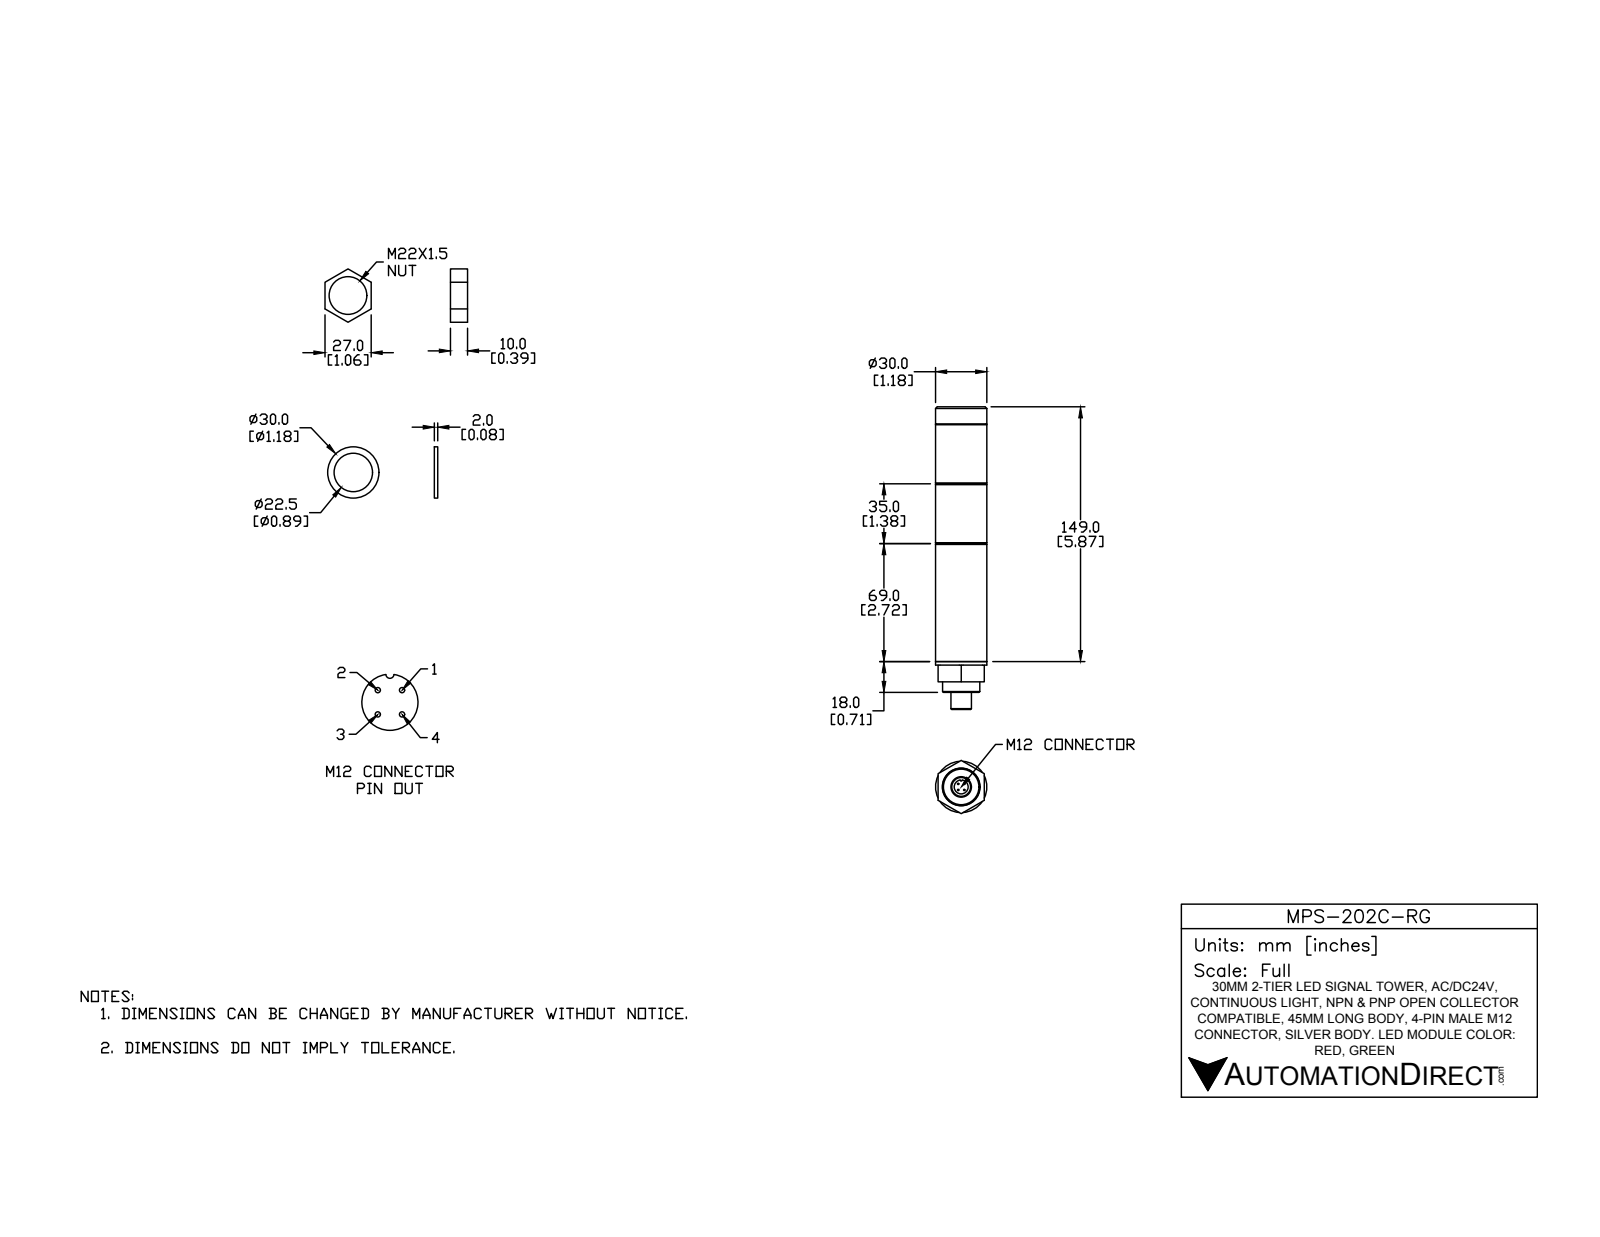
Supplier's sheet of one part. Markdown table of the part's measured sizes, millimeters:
| quantity | value |
| --- | --- |
| part name | MPS-202C-RG |
| STEP written by | SolidWorks 2016 (AUTOMOTIVE_DESIGN) |
| units | millimeters |
| bodies | 11 solids, 106 faces (43 planar, 37 cylindrical, 26 other) |
| overall size | 177 × 31.18 × 30 |
| volume | 104 467 mm³ |
| surface area | 27 501 mm² |
| round holes (diameter × count) | 3.2 × 1, 7.7 × 1, 8.2 × 1, 20.7 × 1, 22 × 1 |
| round bosses / shafts (diameter × count) | 0.75 × 4, 30 × 1, 21.8 × 1, 12 × 1, 5 × 1 |
| partial cylindrical surfaces (radius × count) | 0.6 × 1 |
| main face-to-face distances | 35, 70, 69, 104, 139, 71, 106, 10, 2, 141 |
